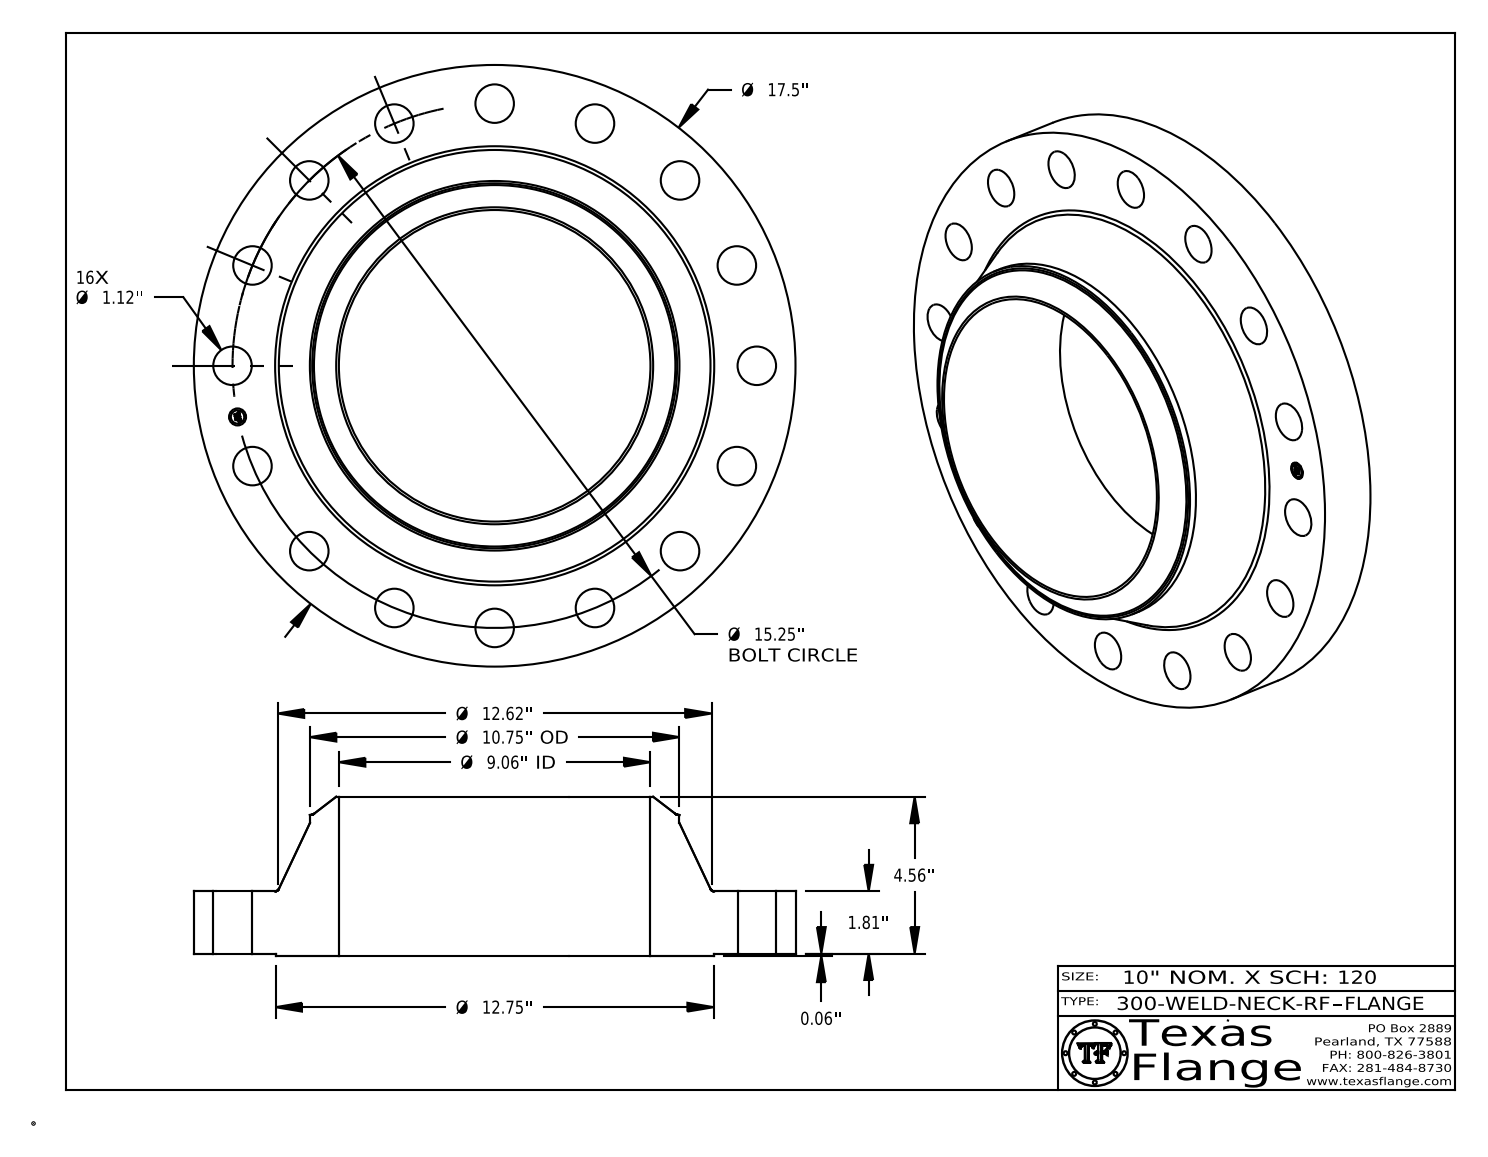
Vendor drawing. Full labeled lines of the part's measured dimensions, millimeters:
Part name (STEP PRODUCT): 300-WELD-NECK-RF
STEP written by: CATIA V5 STEP AP214 (AUTOMOTIVE_DESIGN)
Units: millimetres
Bodies: 1 solid, 439 faces (369 planar, 60 cylindrical, 10 other)
Overall size (bounding box): 444.5 × 444.5 × 117.4
Volume: 6 429 000 mm³ · Surface area: 461 400 mm²
Round holes (diameter × count): ⌀28.4 ×16, ⌀12.6 ×1, ⌀230.2 ×1
Round bosses / shafts (diameter × count): ⌀0.8 ×8, ⌀444.5 ×1, ⌀323.9 ×1, ⌀273.1 ×1, ⌀9.9 ×1
Main face-to-face distances: 46, 1.6, 47.5, 117.4, 115.8, 69.9, 0.4, 47.2, 45.6, 70.2
Hole centre spacings: 215.2, 273.9, 379.9, 357.9, 193.7, 75.6, 75.6, 148.2
